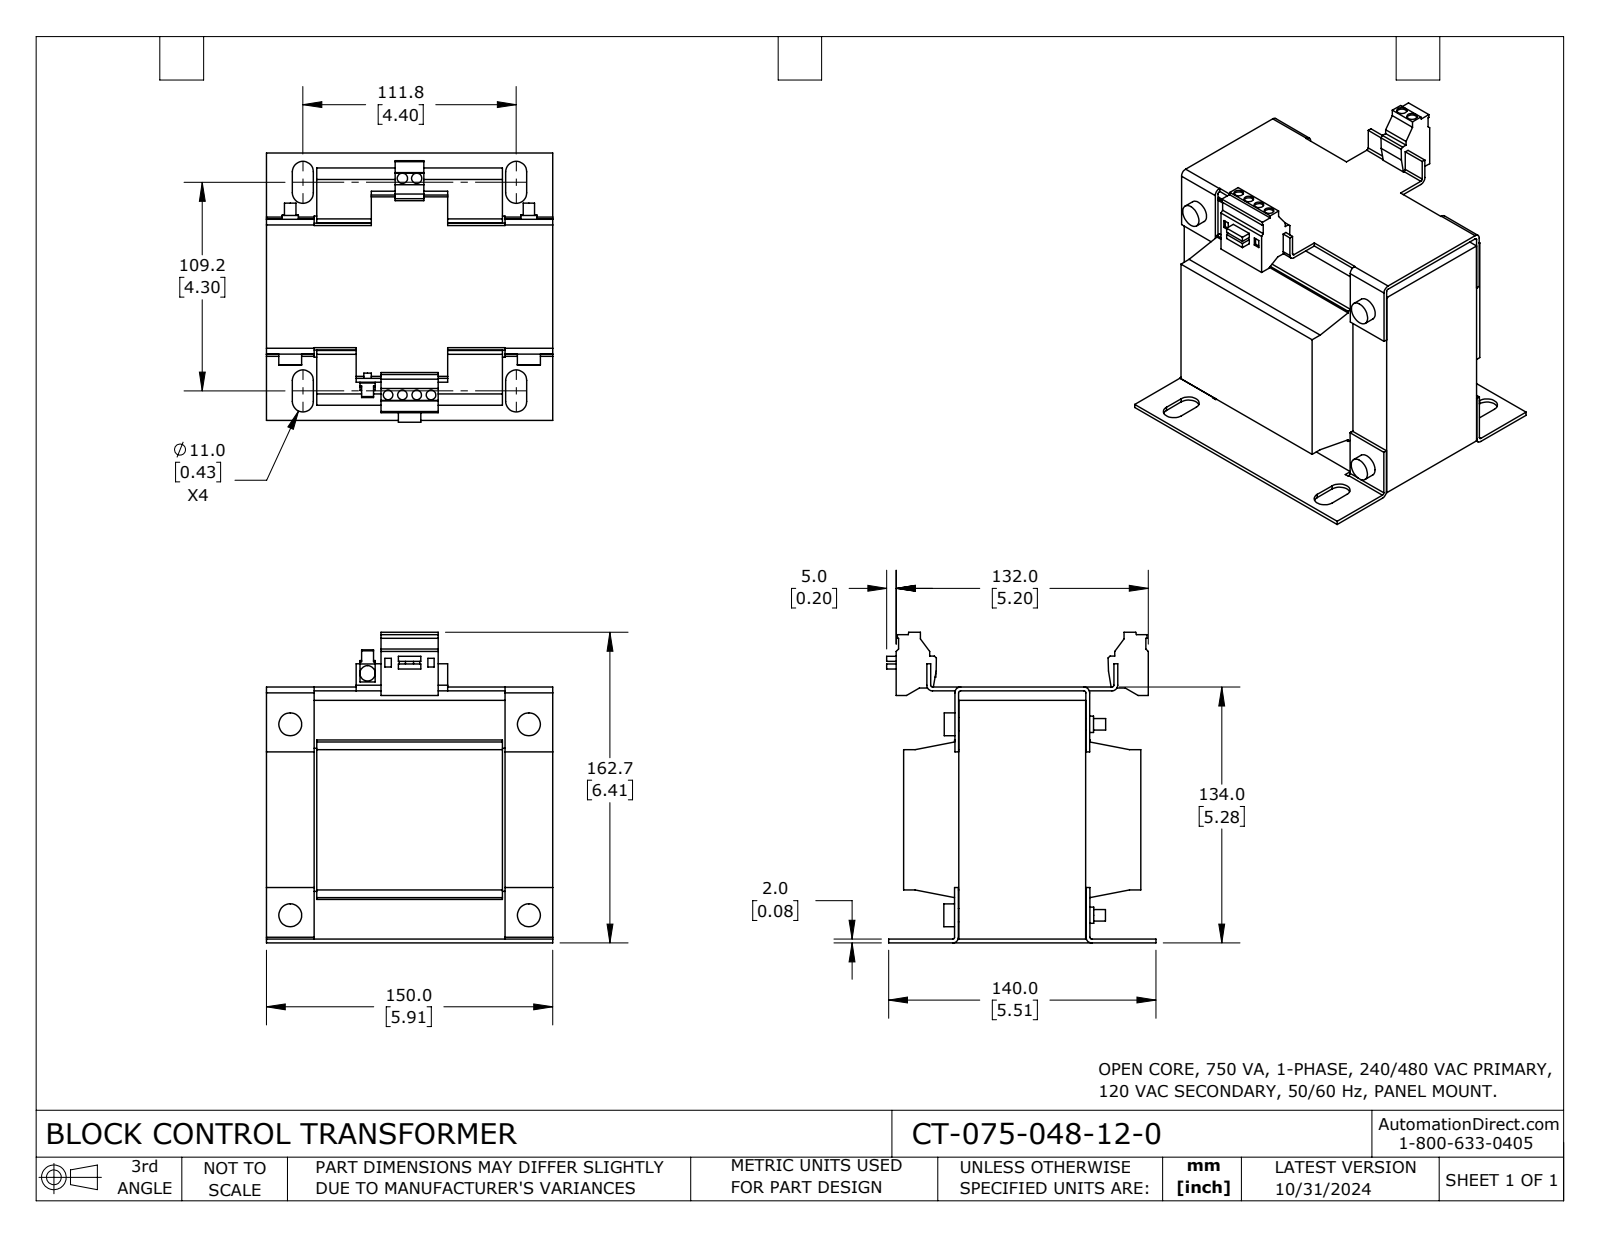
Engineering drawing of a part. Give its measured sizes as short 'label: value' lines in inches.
name: CT-075-048-12-0
written by: SolidWorks 2023 (CONFIG_CONTROL_DESIGN)
unit: in
bodies: 1 solid, 325 faces (233 planar, 92 cylindrical, 0 other)
size: 6.406 × 5.906 × 5.551
volume: 107.3 in³; area: 304.8 in²
holes: 4× ⌀0.197, 2× ⌀0.213
bosses: 4× ⌀0.472, 4× ⌀0.335, 4× ⌀0.276, 4× ⌀0.236, 1× ⌀0.315, 1× ⌀0.157
rounds: 8× R0.217, 6× R0.039, 6× R0.118
face distances: 0.079, 5.197, 4.921, 1.039, 4.866, 0.984, 1.138, 3.756, 3.937, 2.618
hole spacings: 0.295, 4.474, 0.591, 4.465, 4.504, 0.886
